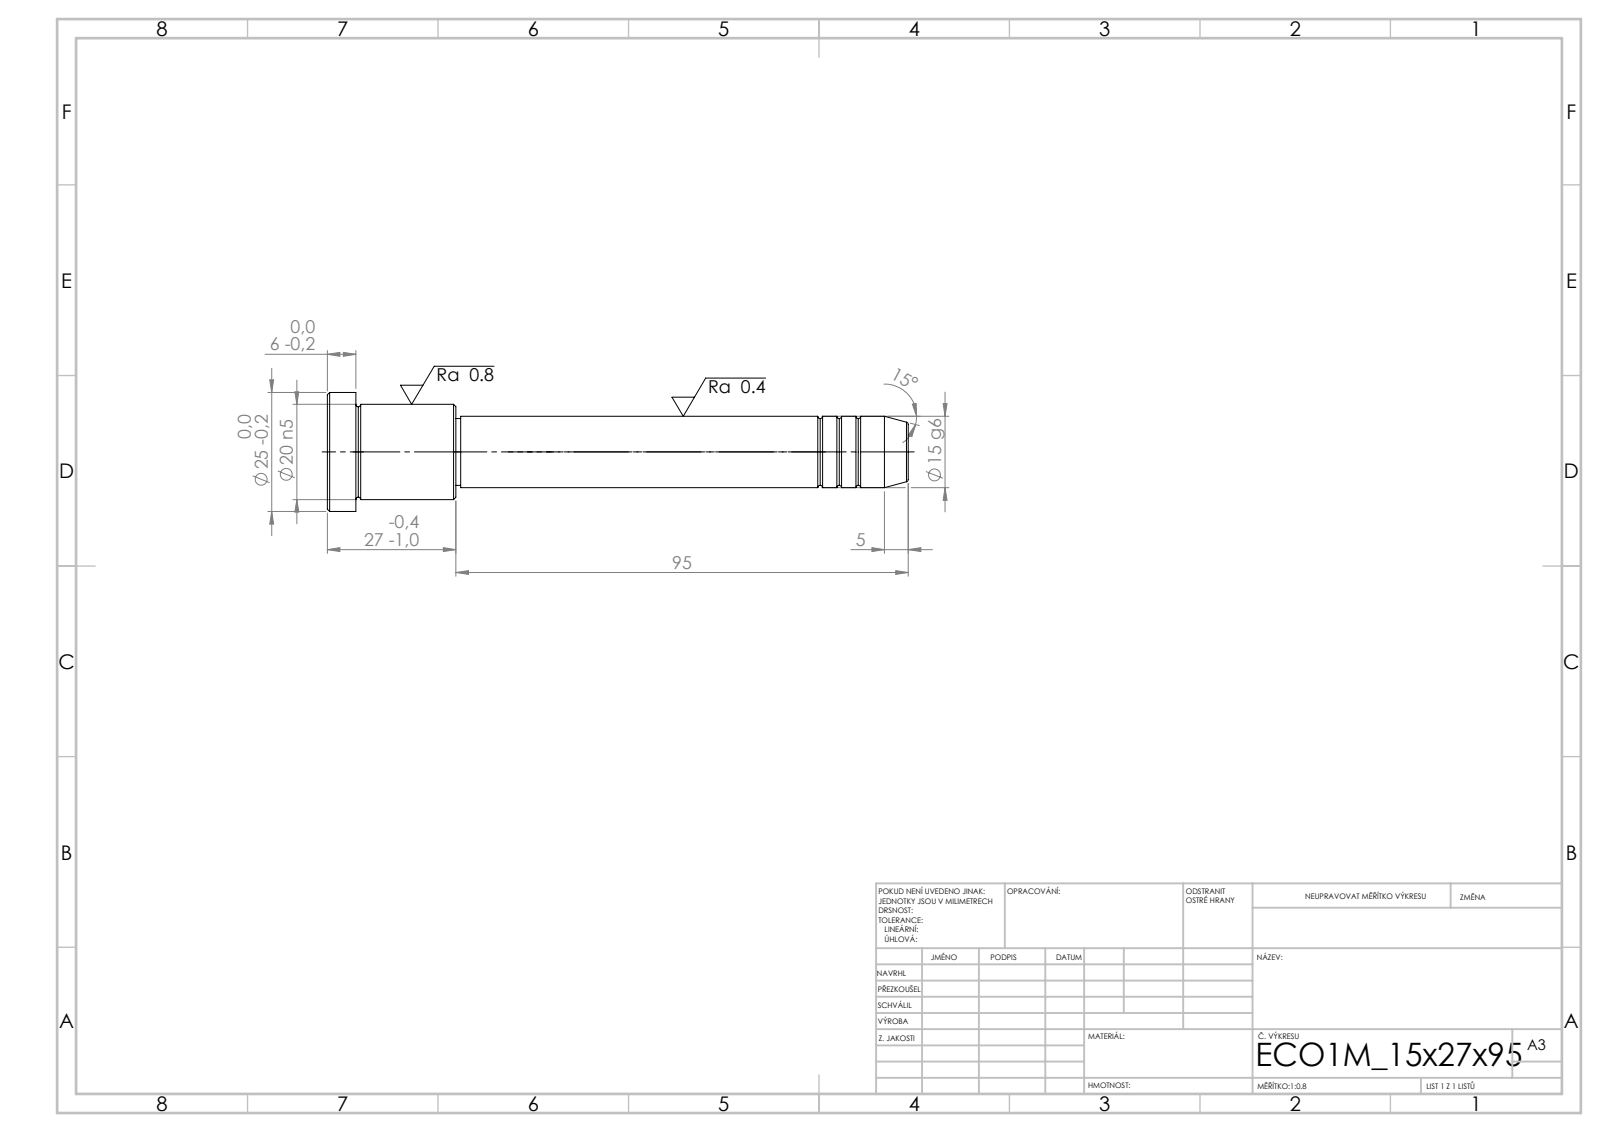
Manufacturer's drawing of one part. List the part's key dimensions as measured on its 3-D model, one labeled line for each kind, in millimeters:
STEP written by: SolidWorks 2019 (CONFIG_CONTROL_DESIGN)
Units: millimetres
Bodies: 1 solid, 43 faces (5 planar, 14 cylindrical, 24 other)
Overall size (bounding box): 122 × 25 × 25
Volume: 26 063 mm³ · Surface area: 7 278 mm²
Round bosses / shafts (diameter × count): ⌀25 ×1, ⌀20 ×1, ⌀15 ×1, ⌀14 ×1
Main face-to-face distances: 6, 21, 27, 95, 116, 122, 94, 1, 22, 28
